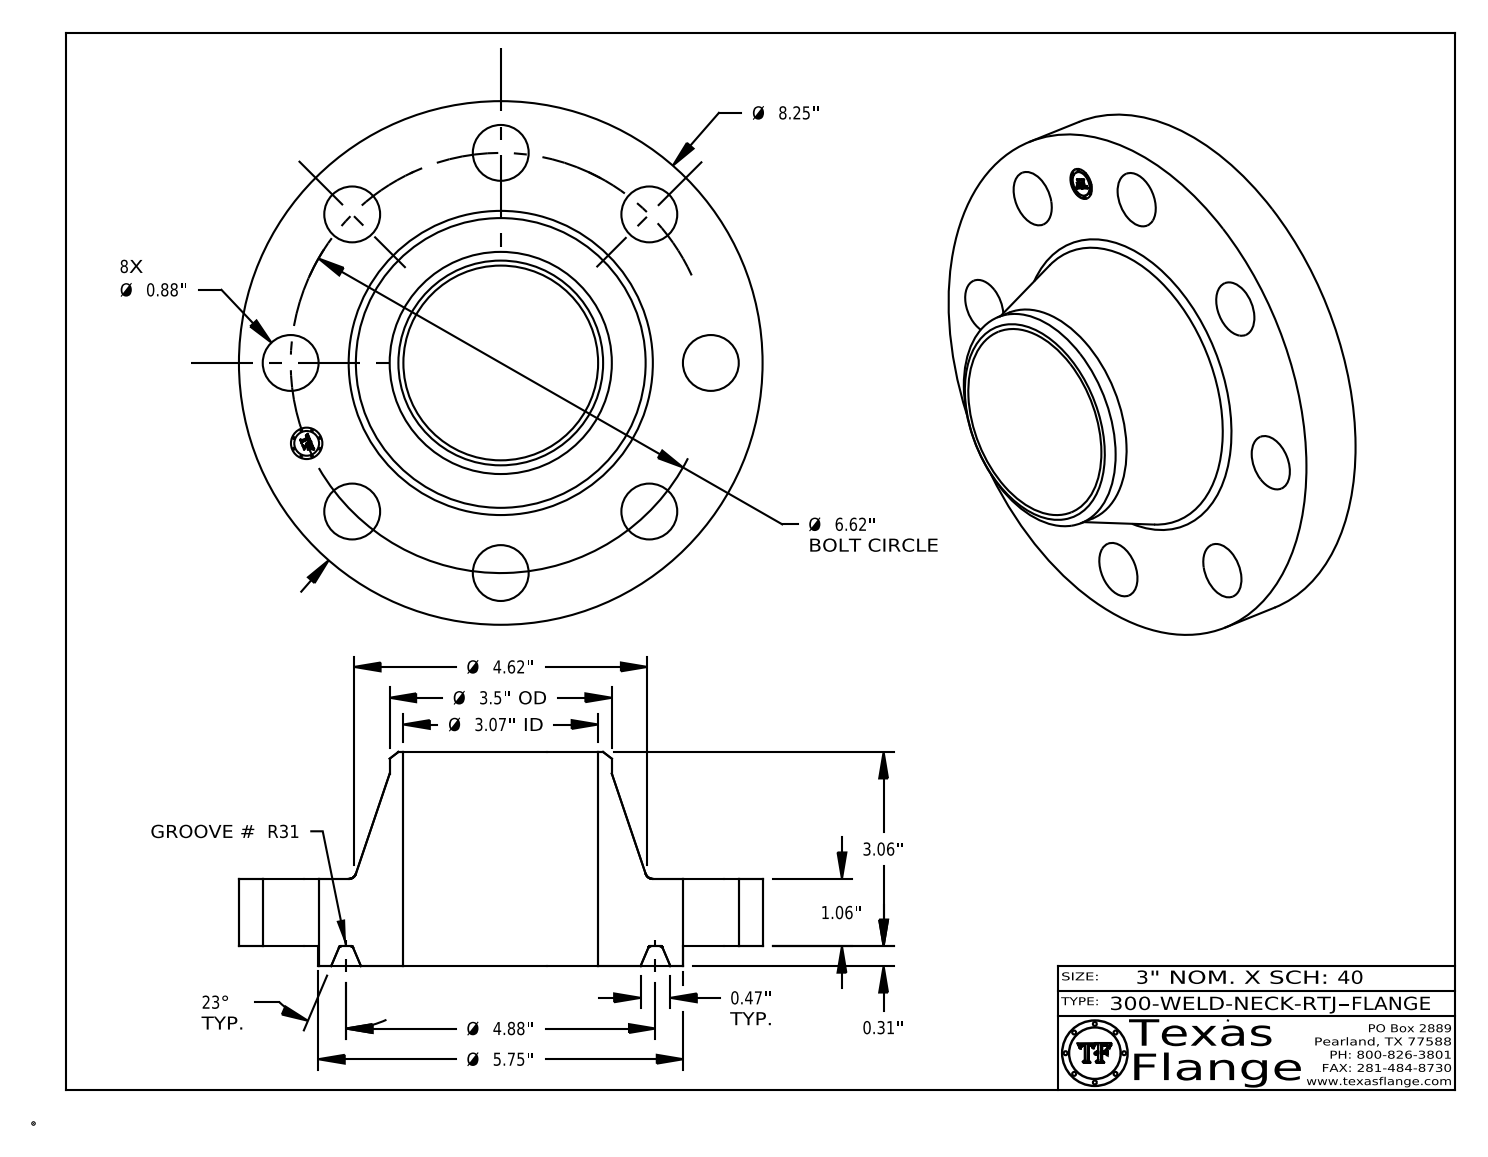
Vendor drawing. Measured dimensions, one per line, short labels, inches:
name: 300-WELD-NECK-RTJ
written by: CATIA V5 STEP AP214 (AUTOMOTIVE_DESIGN)
unit: in
bodies: 1 solid, 437 faces (371 planar, 52 cylindrical, 14 other)
size: 8.25 × 8.25 × 3.373
volume: 57.92 in³; area: 195.6 in²
holes: 8× ⌀0.88, 1× ⌀0.495, 1× ⌀3.068
bosses: 8× ⌀0.03, 1× ⌀8.25, 1× ⌀5.75, 1× ⌀3.5, 1× ⌀0.39
face distances: 1.06, 0.313, 1.373, 3.373, 3.06, 2, 0.015, 1.358, 1.045, 2.015
hole spacings: 3.31, 2.533, 6.116, 4.681, 4.681, 1.291, 3.678, 6.493
